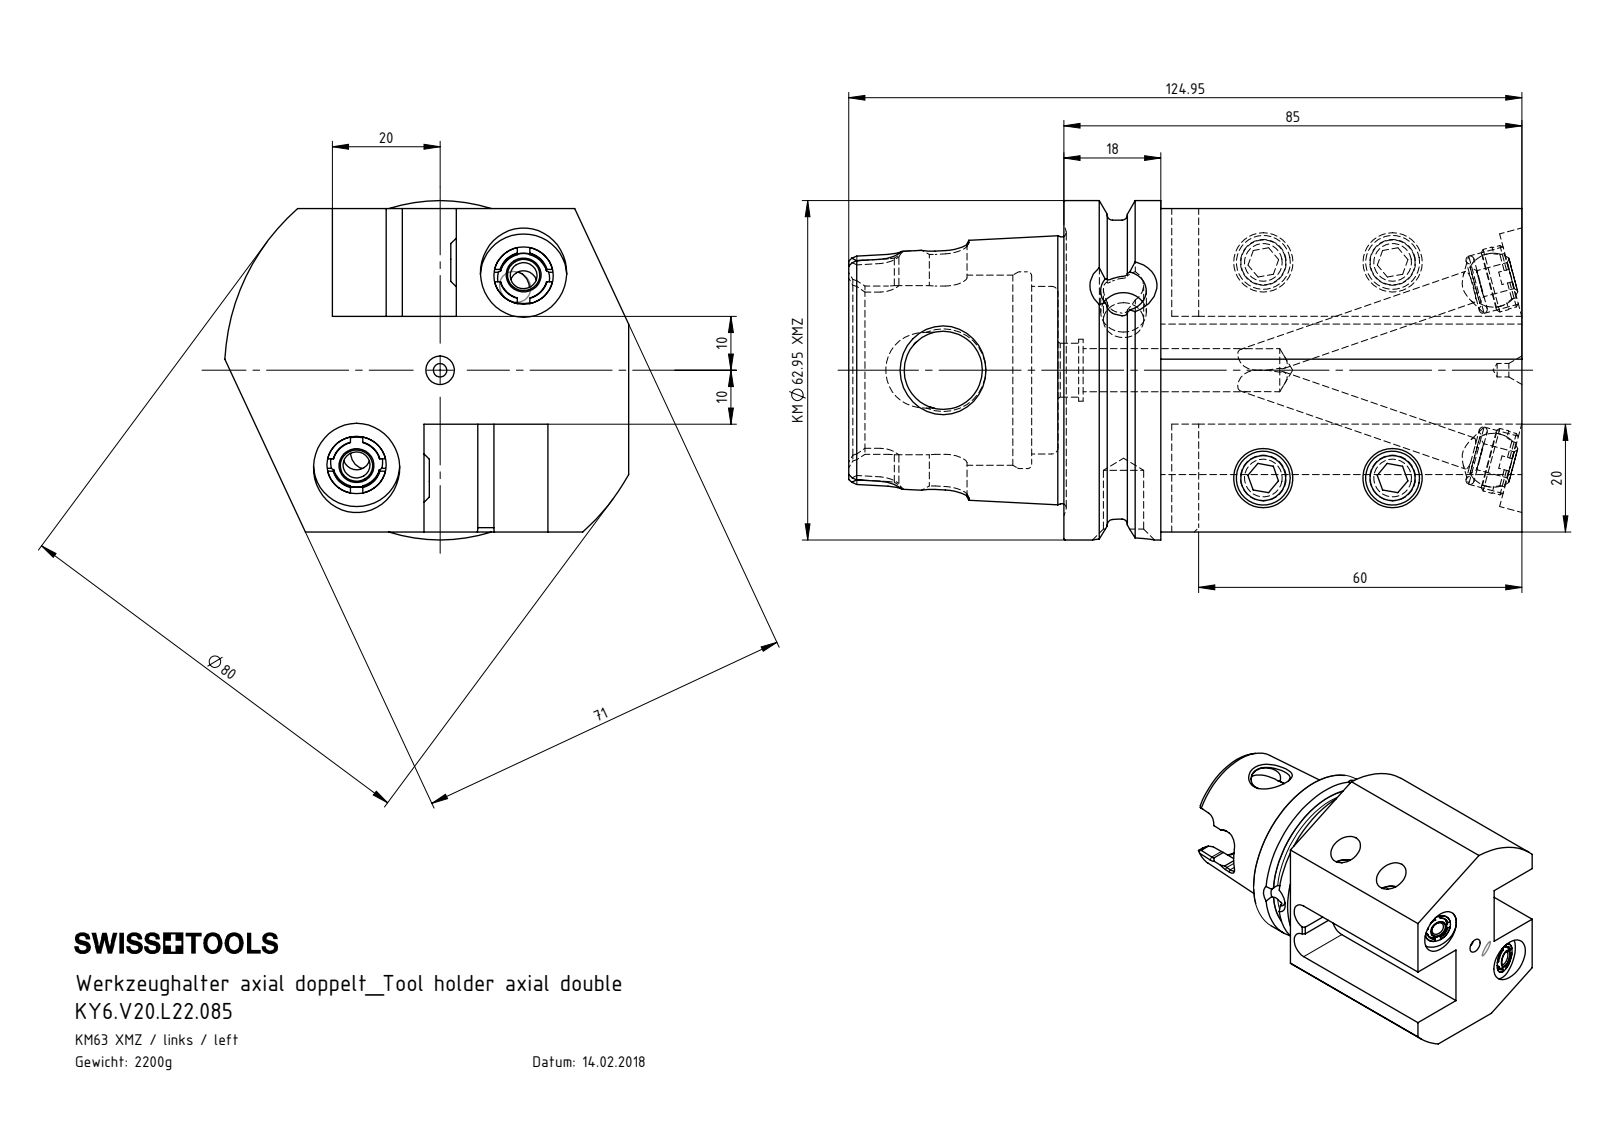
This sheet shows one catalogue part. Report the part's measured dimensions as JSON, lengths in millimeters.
{"part_name": "KY6.V20.L22.085; ISO 4026 - M10 x 20; DIN 3771 - 8x1.5; KU1-U12.002.010 (+3 more)", "step_written_by": "SolidWorks 2017 (CONFIG_CONTROL_DESIGN)", "units": "millimeters", "bodies": {"solids": 11, "faces": 399, "planar": 124, "cylindrical": 109, "other": 166}, "overall_size": [124.95, 74.95, 62.95], "volume_mm3": 280217, "surface_area_mm2": 53556, "round_holes": [[11, 6], [8.5, 4], [10, 3], [5, 2], [6, 2], [7.47, 2], [16, 2], [2.5, 1], [8, 1], [8.47, 1], [11.5, 1], [14.5, 1]], "round_bosses_or_shafts": [[10, 4], [12, 2], [62.95, 1], [55.7, 1]], "partial_cylinders_radius": [[4, 6], [5, 4], [4.4, 2], [7.04, 2], [40, 1]], "face_to_face_distances": [20, 40, 17, 23, 60, 70.65, 6, 15, 55, 38], "hole_center_spacings": [24, 40, 46.65, 62.68, 85.76]}
